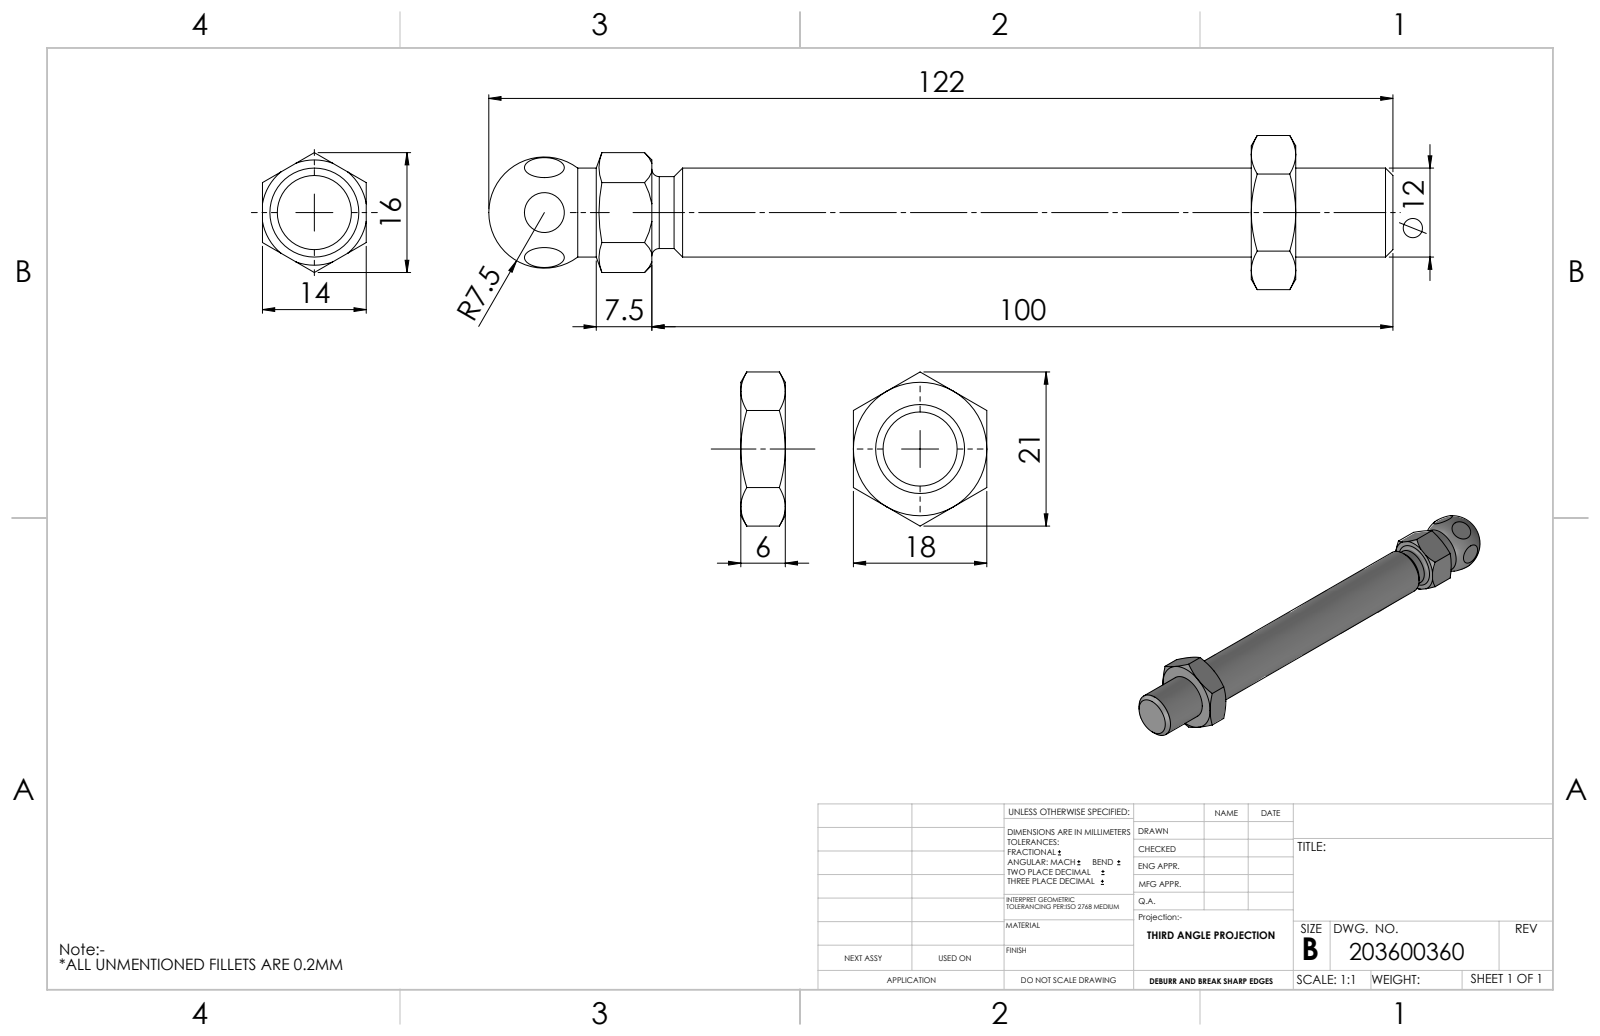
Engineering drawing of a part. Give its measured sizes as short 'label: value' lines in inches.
name: 203600360
written by: SolidWorks 2014 (AUTOMOTIVE_DESIGN)
unit: in
bodies: 2 solids, 66 faces (22 planar, 10 cylindrical, 34 other)
size: 4.803 × 0.819 × 0.709
volume: 0.94 in³; area: 9.13 in²
holes: 1× ⌀0.402
bosses: 1× ⌀0.472, 1× ⌀0.382
face distances: 0.079, 0.63, 0.551, 0.709, 0.236, 0.752, 0.516, 3.185, 3.421, 3.937
